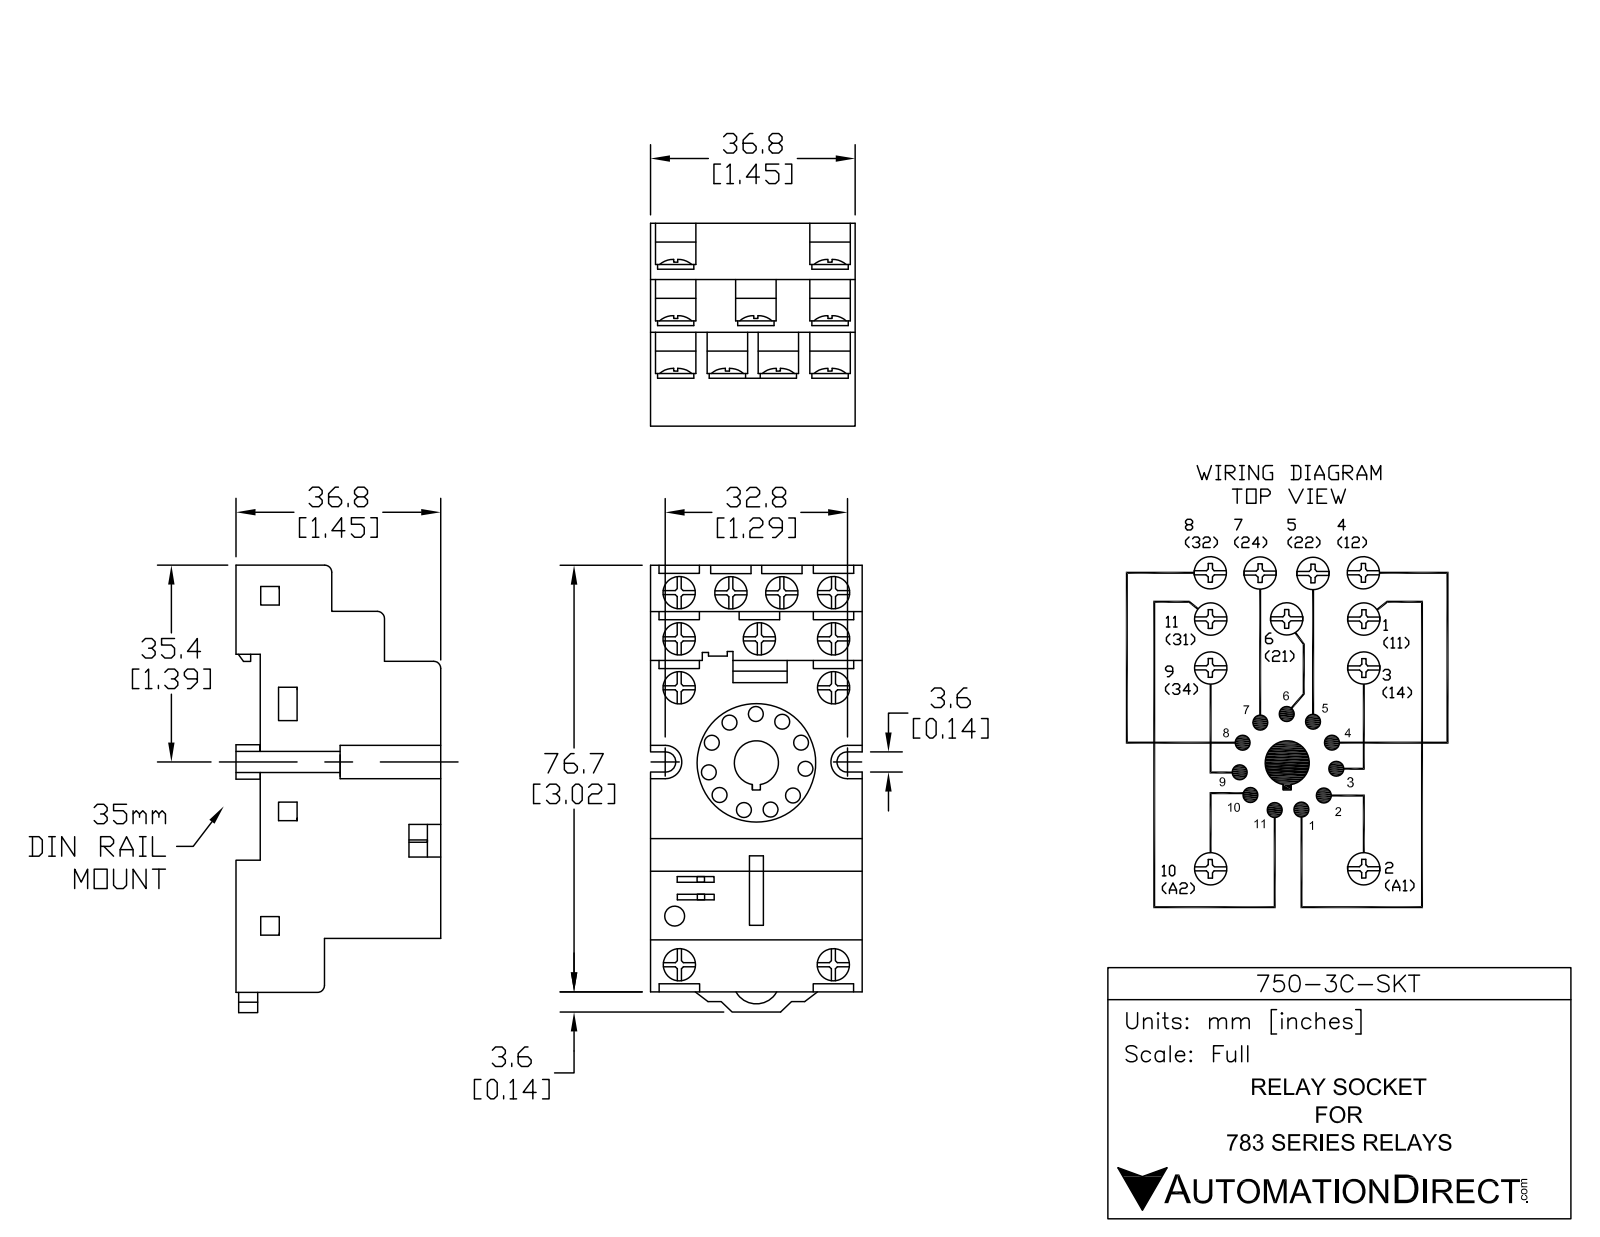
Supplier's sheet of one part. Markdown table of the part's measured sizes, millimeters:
| quantity | value |
| --- | --- |
| part name | 750-3C-SKT |
| STEP written by | SolidWorks 2013 (AUTOMOTIVE_DESIGN) |
| units | millimeters |
| bodies | 1 solid, 488 faces (367 planar, 121 cylindrical, 0 other) |
| overall size | 81.8 × 38.1 × 36.6 |
| volume | 78 070 mm³ |
| surface area | 18 420 mm² |
| round holes (diameter × count) | 2.7 × 11, 5.3 × 11, 3.2 × 1, 8.2 × 1, 21.3 × 1 |
| partial cylindrical surfaces (radius × count) | 0.4 × 41, 0.6 × 4, 0.7 × 4, 1.5 × 2, 1.8 × 2, 3 × 2, 3.6 × 1 |
| main face-to-face distances | 38.1, 3.9, 36.6, 32.7, 36.6, 1.3, 20.8, 32.6, 9.4, 9.9 |
| hole center spacings | 8.9, 17.6, 9.6, 13.4, 5, 16.2, 9.4, 9.6 |
